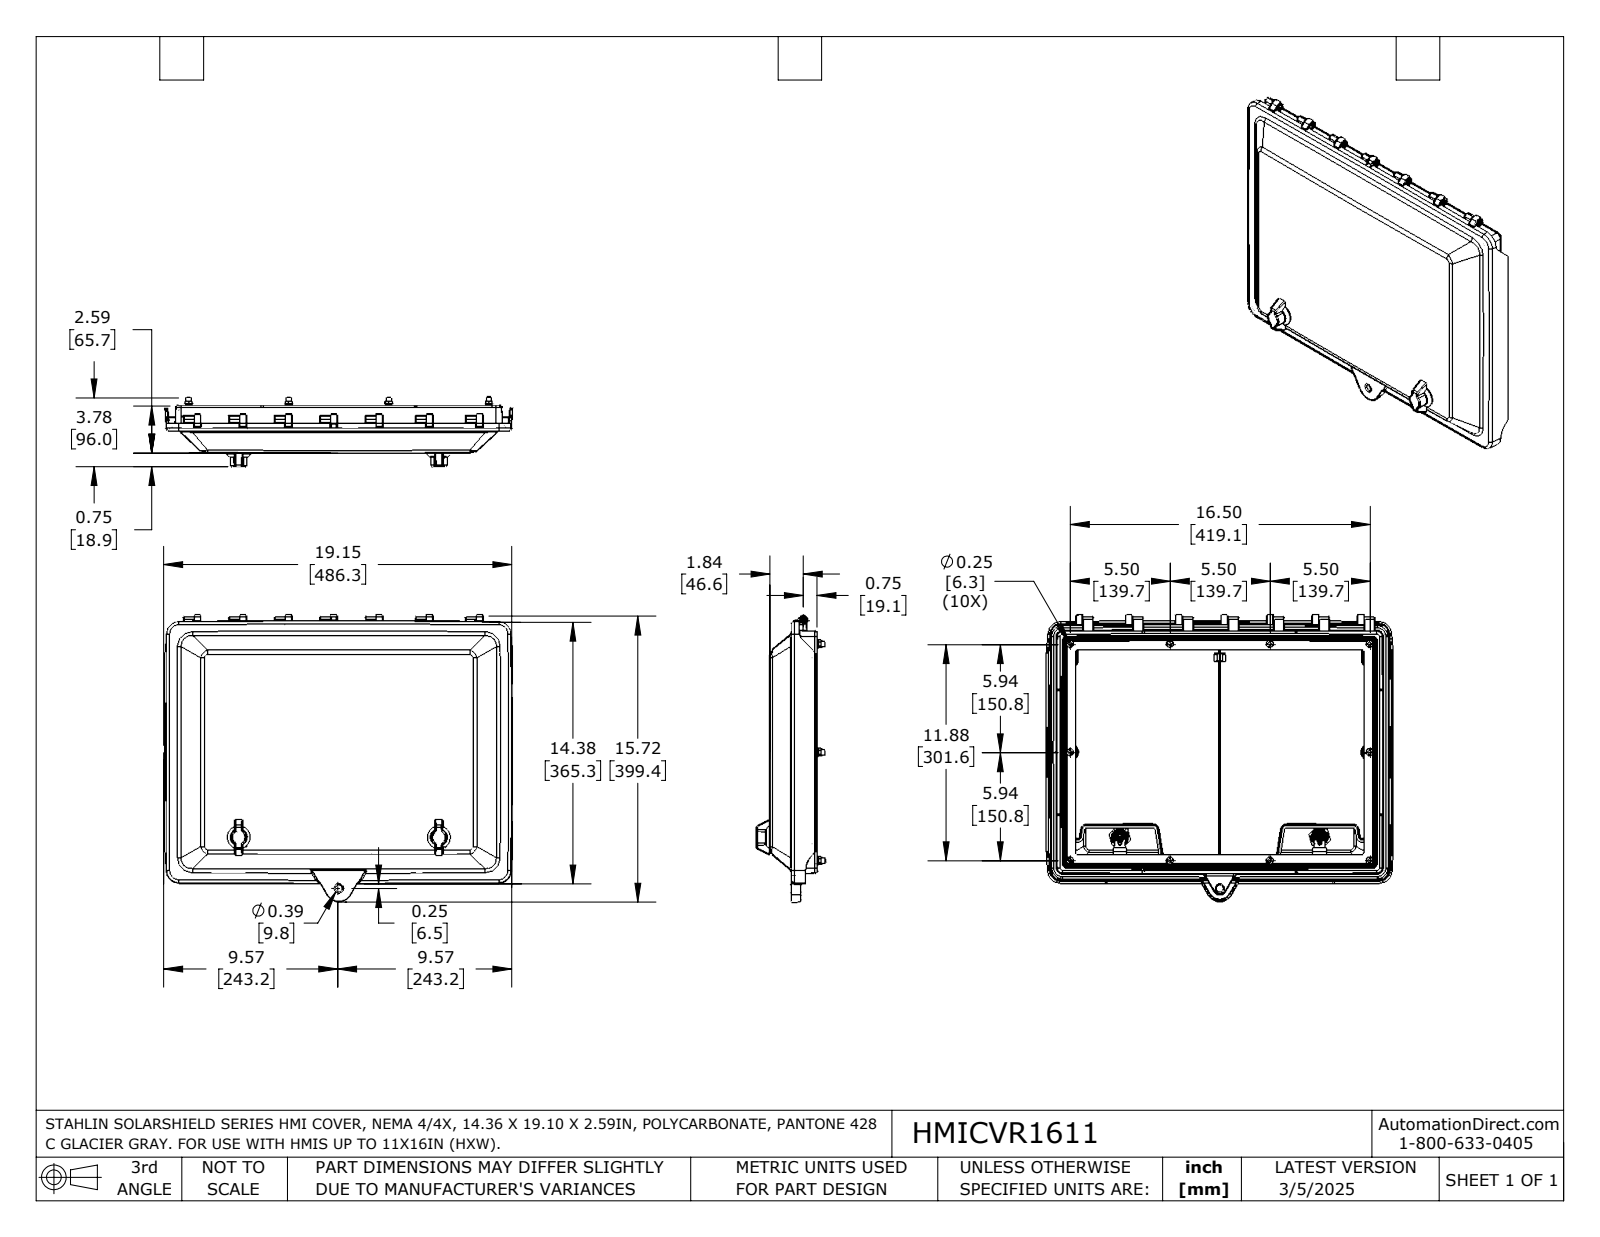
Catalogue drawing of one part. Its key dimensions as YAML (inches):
part_name: "HMICVR1611"
step_written_by: "SolidWorks 2024 (AUTOMOTIVE_DESIGN)"
units: inches
bodies: {solids: 58, faces: 3451, planar: 1075, cylindrical: 770, other: 1606}
overall_size: [19.146, 15.724, 3.831]
volume: 103.7
surface_area: 1603
round_holes:
  - {diameter: 0.197, count: 12}
  - {diameter: 0.19, count: 9}
  - {diameter: 0.083, count: 2}
  - {diameter: 0.168, count: 2}
  - {diameter: 0.201, count: 2}
  - {diameter: 0.236, count: 2}
  - {diameter: 0.315, count: 2}
  - {diameter: 0.591, count: 2}
  - {diameter: 0.802, count: 2}
  - {diameter: 0.846, count: 2}
  - {diameter: 0.328, count: 1}
  - {diameter: 0.37, count: 1}
round_bosses_or_shafts:
  - {diameter: 0.394, count: 10}
  - {diameter: 0.373, count: 10}
  - {diameter: 0.2, count: 10}
  - {diameter: 1.26, count: 2}
  - {diameter: 0.78, count: 2}
  - {diameter: 0.531, count: 2}
  - {diameter: 0.37, count: 2}
  - {diameter: 0.3, count: 2}
partial_cylinders:
  - {radius: 0.02, count: 120}
  - {radius: 0.012, count: 61}
  - {radius: 0.03, count: 56}
  - {radius: 0.02, count: 40}
  - {radius: 0.04, count: 25}
  - {radius: 0.05, count: 12}
  - {radius: 0.059, count: 12}
  - {radius: 0.106, count: 8}
face_to_face_distances: [0.25, 0.125, 1, 1.25, 0.125, 1.125, 1.375, 1.23, 0.98, 0.02]
hole_center_spacings: [5.5, 11, 13.087, 2.787, 3.03, 5.937, 8.093, 10.953]
